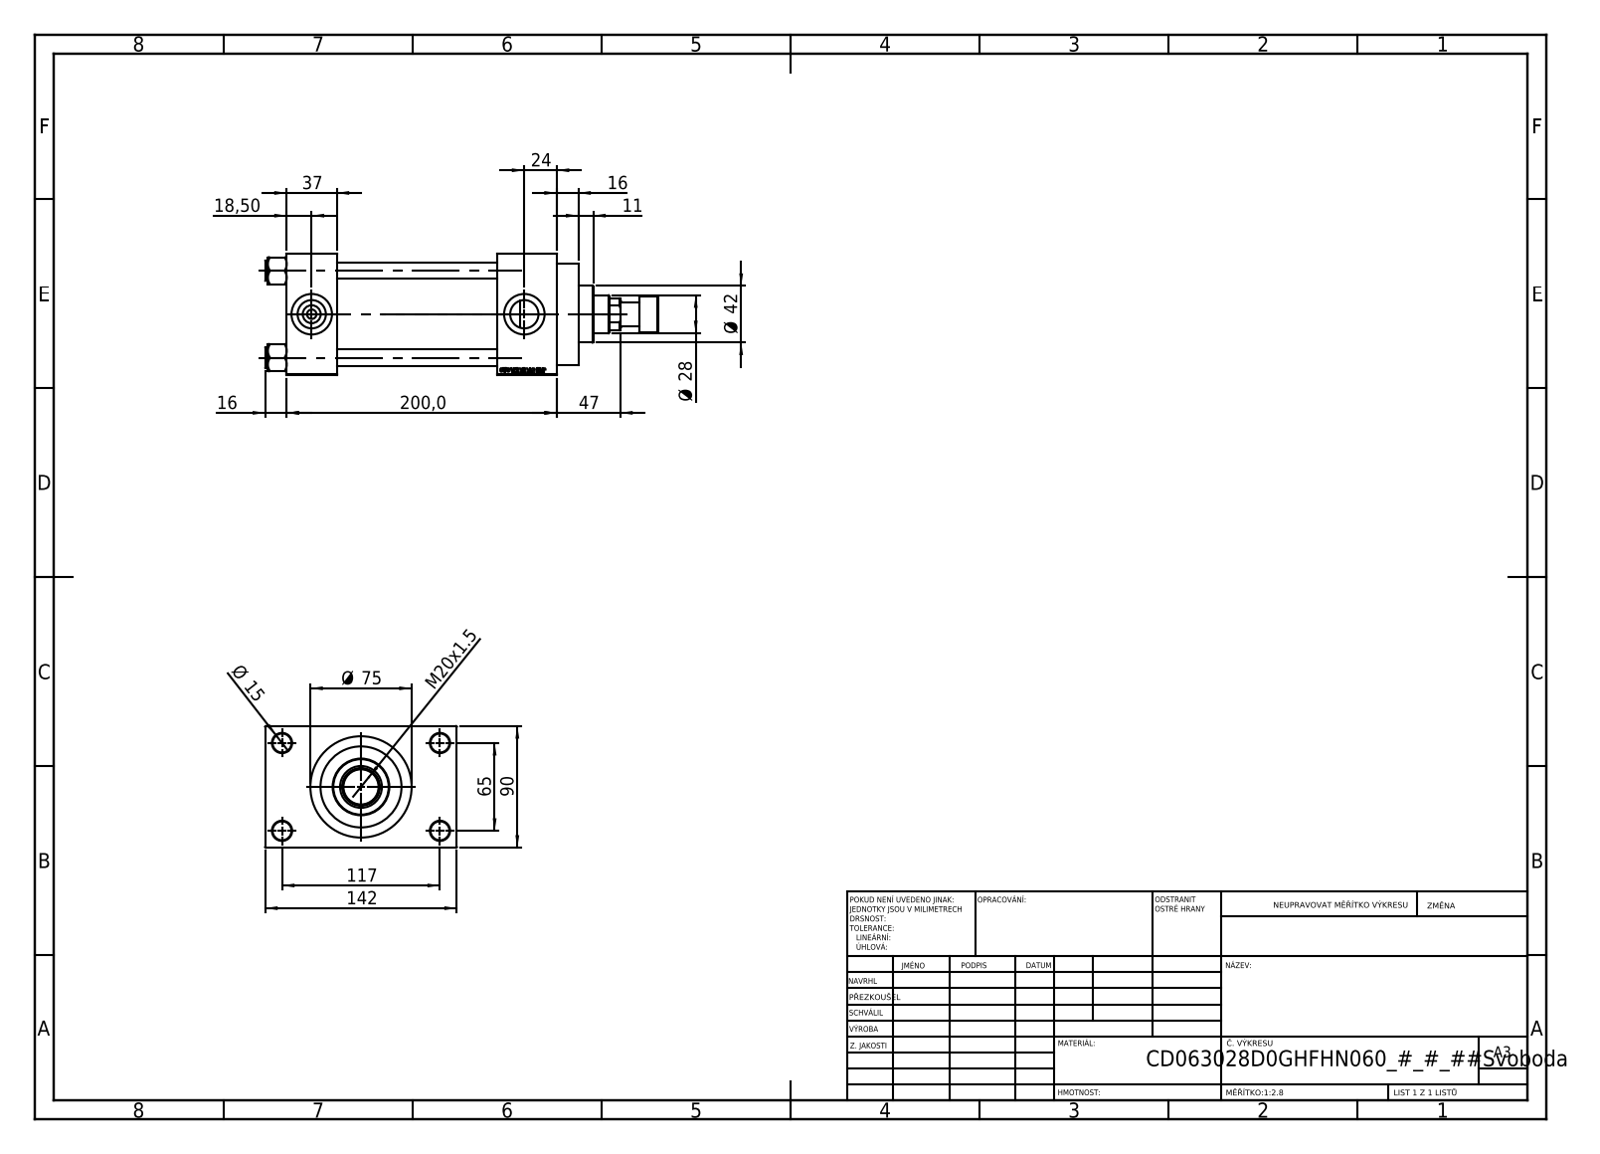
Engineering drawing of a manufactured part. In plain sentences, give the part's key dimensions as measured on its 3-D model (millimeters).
The part is named "V215CD_VCP_D; V215CD_D_TYCINKA; V215CD_VC_A; V215CD_D_Body (+2 more)". Its 3-D file was written by "SolidWorks 2019 (CONFIG_CONTROL_DESIGN)". It is 12 solids with 1117 faces: 501 planar, 92 cylindrical and 524 other. Overall it measures 291 by 142 by 90 millimeters. Its volume is 1 209 000 cubic millimeters and its surface area 242 777 square millimeters. Round holes: 4 of diameter 12, 4 of diameter 14, 2 of diameter 7, 2 of diameter 20.96, 2 of diameter 30, 1 of diameter 18.5, 1 of diameter 28, 1 of diameter 31, 1 of diameter 50, 1 of diameter 60, 1 of diameter 63. Round bosses or shafts: 4 of diameter 15, 1 of diameter 75, 1 of diameter 69, 1 of diameter 42, 1 of diameter 27, 1 of diameter 18. The main face-to-face distances are 90, 119, 37, 156, 163, 200, 44, 26, 116, 16. The hole center spacings are 26.35, 45.47, 64.3, 66.92, 69.81, 90.65, 111.34, 65.
